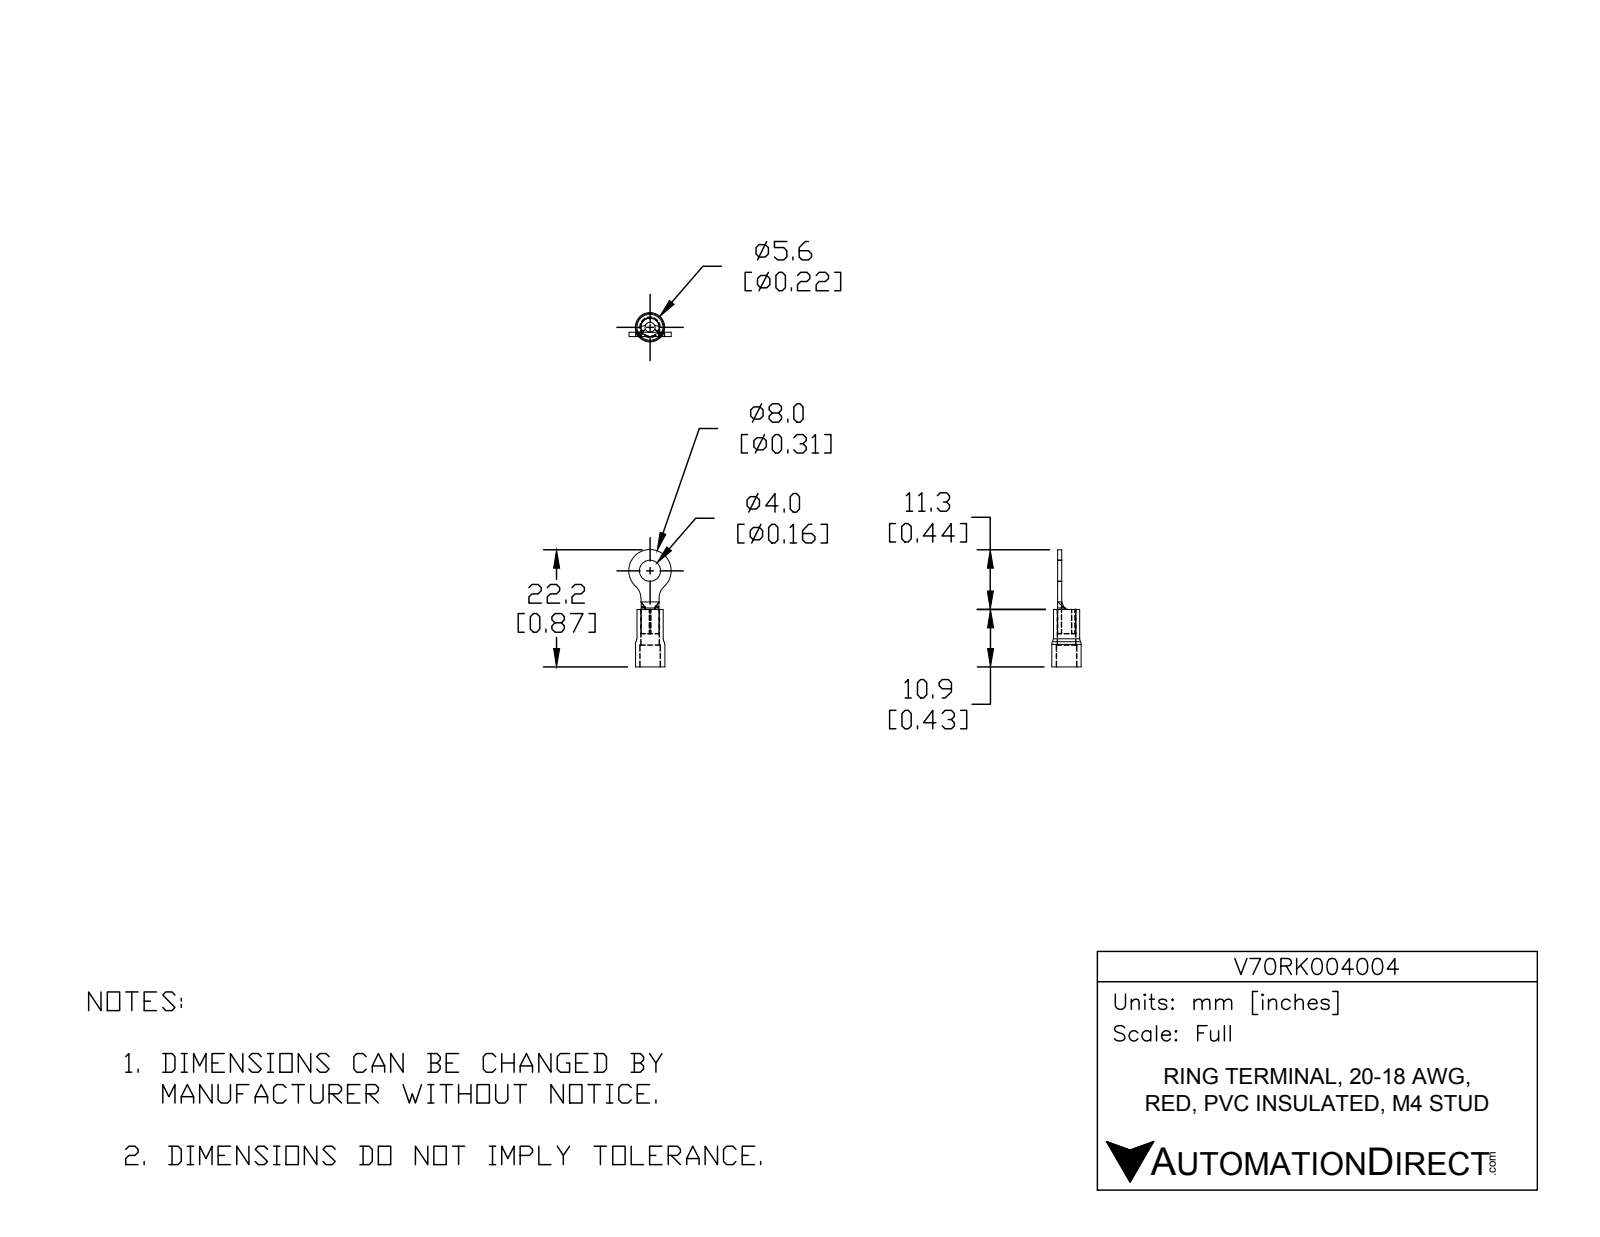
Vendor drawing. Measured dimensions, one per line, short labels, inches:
name: V70RK004004
written by: SolidWorks 2017 (AUTOMOTIVE_DESIGN)
unit: in
bodies: 2 solids, 45 faces (12 planar, 21 cylindrical, 12 other)
size: 0.874 × 0.315 × 0.219
volume: 0.011 in³; area: 0.857 in²
holes: 1× ⌀0.075, 1× ⌀0.138, 1× ⌀0.152, 1× ⌀0.157
bosses: 1× ⌀0.219, 1× ⌀0.195, 1× ⌀0.134
rounds: 2× R0.004, 2× R0.118, 1× R0.157
face distances: 0.031, 0.429, 0.248, 0.181, 0.163, 0.085, 0.266, 0.068, 0.066, 0.067
